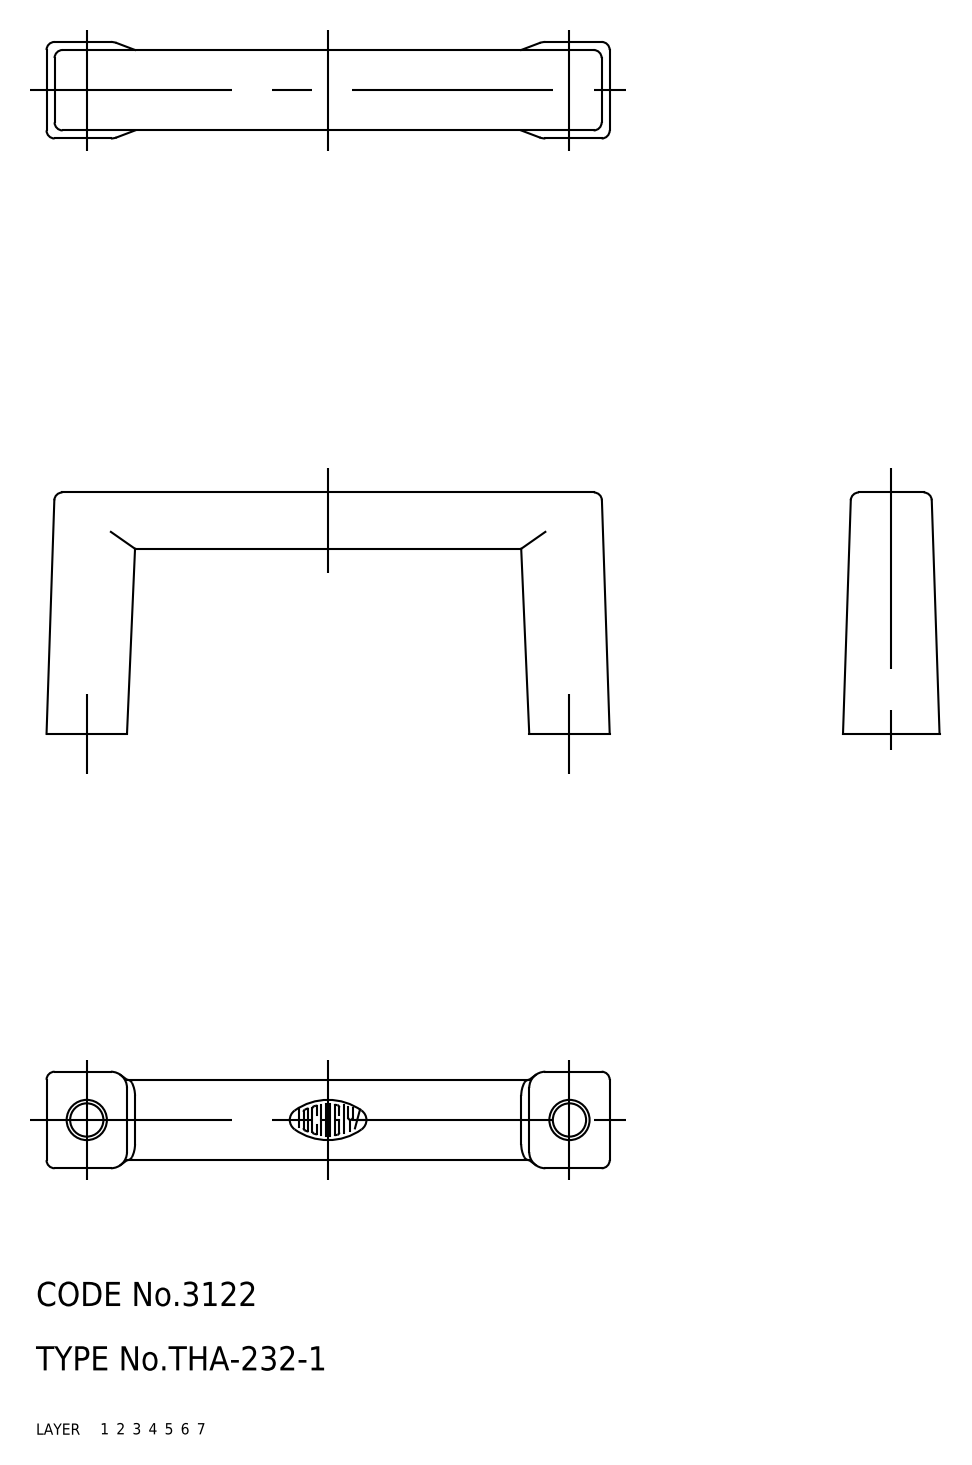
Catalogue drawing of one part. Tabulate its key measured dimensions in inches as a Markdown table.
| quantity | value |
| --- | --- |
| part name | pull |
| STEP written by | CADfix (AUTOMOTIVE_DESIGN) |
| units | inches |
| bodies | 1 solid, 34 faces (0 planar, 0 cylindrical, 34 other) |
| overall size | 2.756 × 1.181 × 0.472 |
| volume | 0.574 in³ |
| surface area | 7.099 in² |
